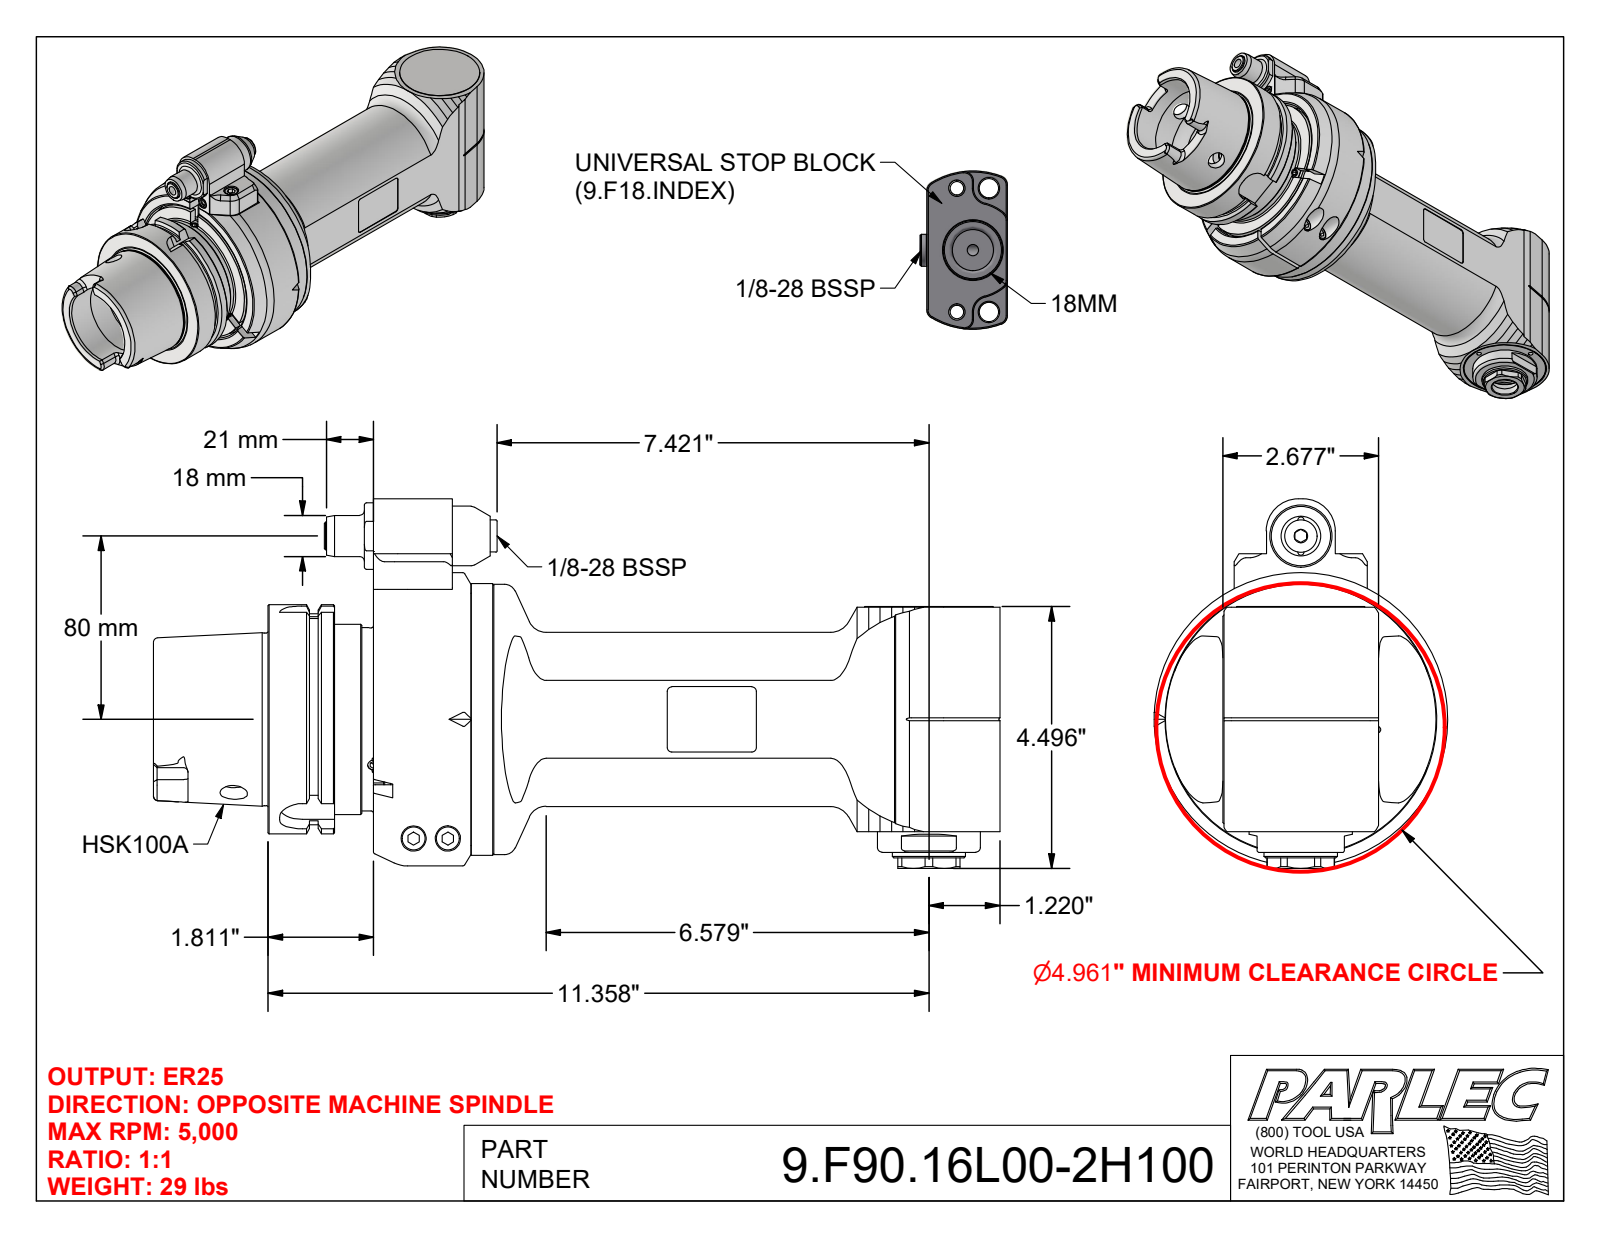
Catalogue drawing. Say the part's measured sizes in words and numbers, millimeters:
The part is named "9.F90.16L00-2H100; 9_GA2_518_2 (Type 2, HSK100, 80mm, 18P); 9_F90_16L00". Its 3-D file was written by "Autodesk Inventor 2022 (AUTOMOTIVE_DESIGN)". It is 5 solids with 637 faces: 266 planar, 164 cylindrical and 207 other. Overall it measures 369.5 by 161.2 by 128 millimeters. Its volume is 2 094 000 cubic millimeters and its surface area 239 200 square millimeters. Round holes: 20 of diameter 10.5, 4 of diameter 3.2, 4 of diameter 5, 3 of diameter 12.5, 2 of diameter 2.6, 2 of diameter 4.2, 2 of diameter 5.3, 2 of diameter 8, 2 of diameter 10.4, 2 of diameter 11, 2 of diameter 12, 1 of diameter 2.5. Round bosses or shafts: 4 of diameter 10, 4 of diameter 6, 2 of diameter 18, 2 of diameter 12, 2 of diameter 2.5, 1 of diameter 128, 1 of diameter 118.6, 1 of diameter 118. Partial cylindrical surfaces (rounded edges, fillets, slot ends): 18 of radius 2, 4 of radius 4, 4 of radius 4.9, 4 of radius 10, 2 of radius 0.4, 2 of radius 0.5, 2 of radius 1, 2 of radius 8. The main face-to-face distances are 68, 5, 35, 37.5, 2.5, 38, 7.5, 3, 42.5, 8.5. The hole center spacings are 46.8, 92.6, 45.3, 56.3, 66.1, 66.1, 81.8, 89.9.
